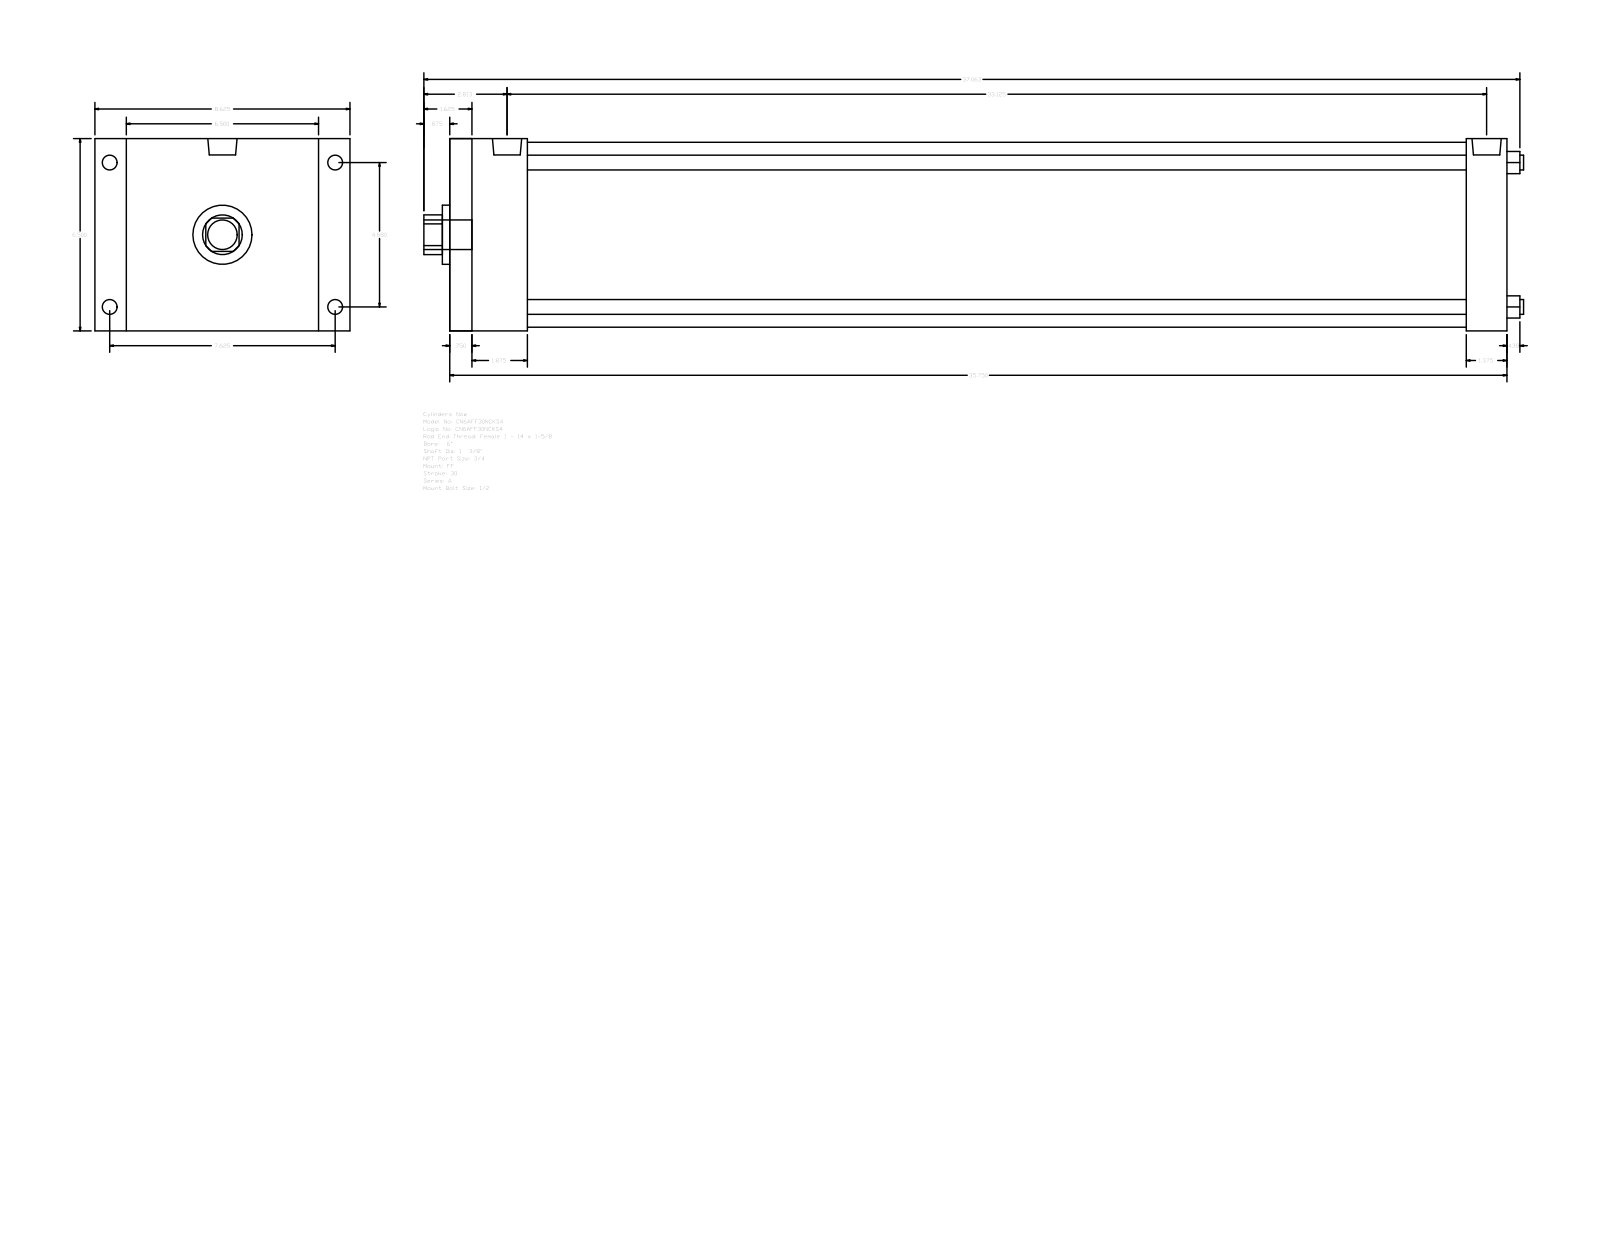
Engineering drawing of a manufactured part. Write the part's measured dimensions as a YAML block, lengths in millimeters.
part_name: "A_FF__0600_1.375"
step_written_by: "GSSL Pune (CONFIG_CONTROL_DESIGN)"
units: millimeters
bodies: {solids: 0, faces: 92, planar: 64, cylindrical: 28, other: 0}
overall_size: [944.56, 219.07, 165.1]
round_holes:
  - {diameter: 12.7, count: 4}
  - {diameter: 34.92, count: 1}
  - {diameter: 50.8, count: 1}
  - {diameter: 158.75, count: 1}
round_bosses_or_shafts:
  - {diameter: 15.08, count: 4}
  - {diameter: 12.7, count: 4}
  - {diameter: 25.12, count: 2}
  - {diameter: 25.4, count: 1}
partial_cylinders:
  - {radius: 17.06, count: 1}
face_to_face_distances: [165.1, 908.04, 19.04, 889, 66.67, 47.63, 841.37, 873.12, 854.08, 806.45]
hole_center_spacings: [87.65, 123.96, 175.31]
